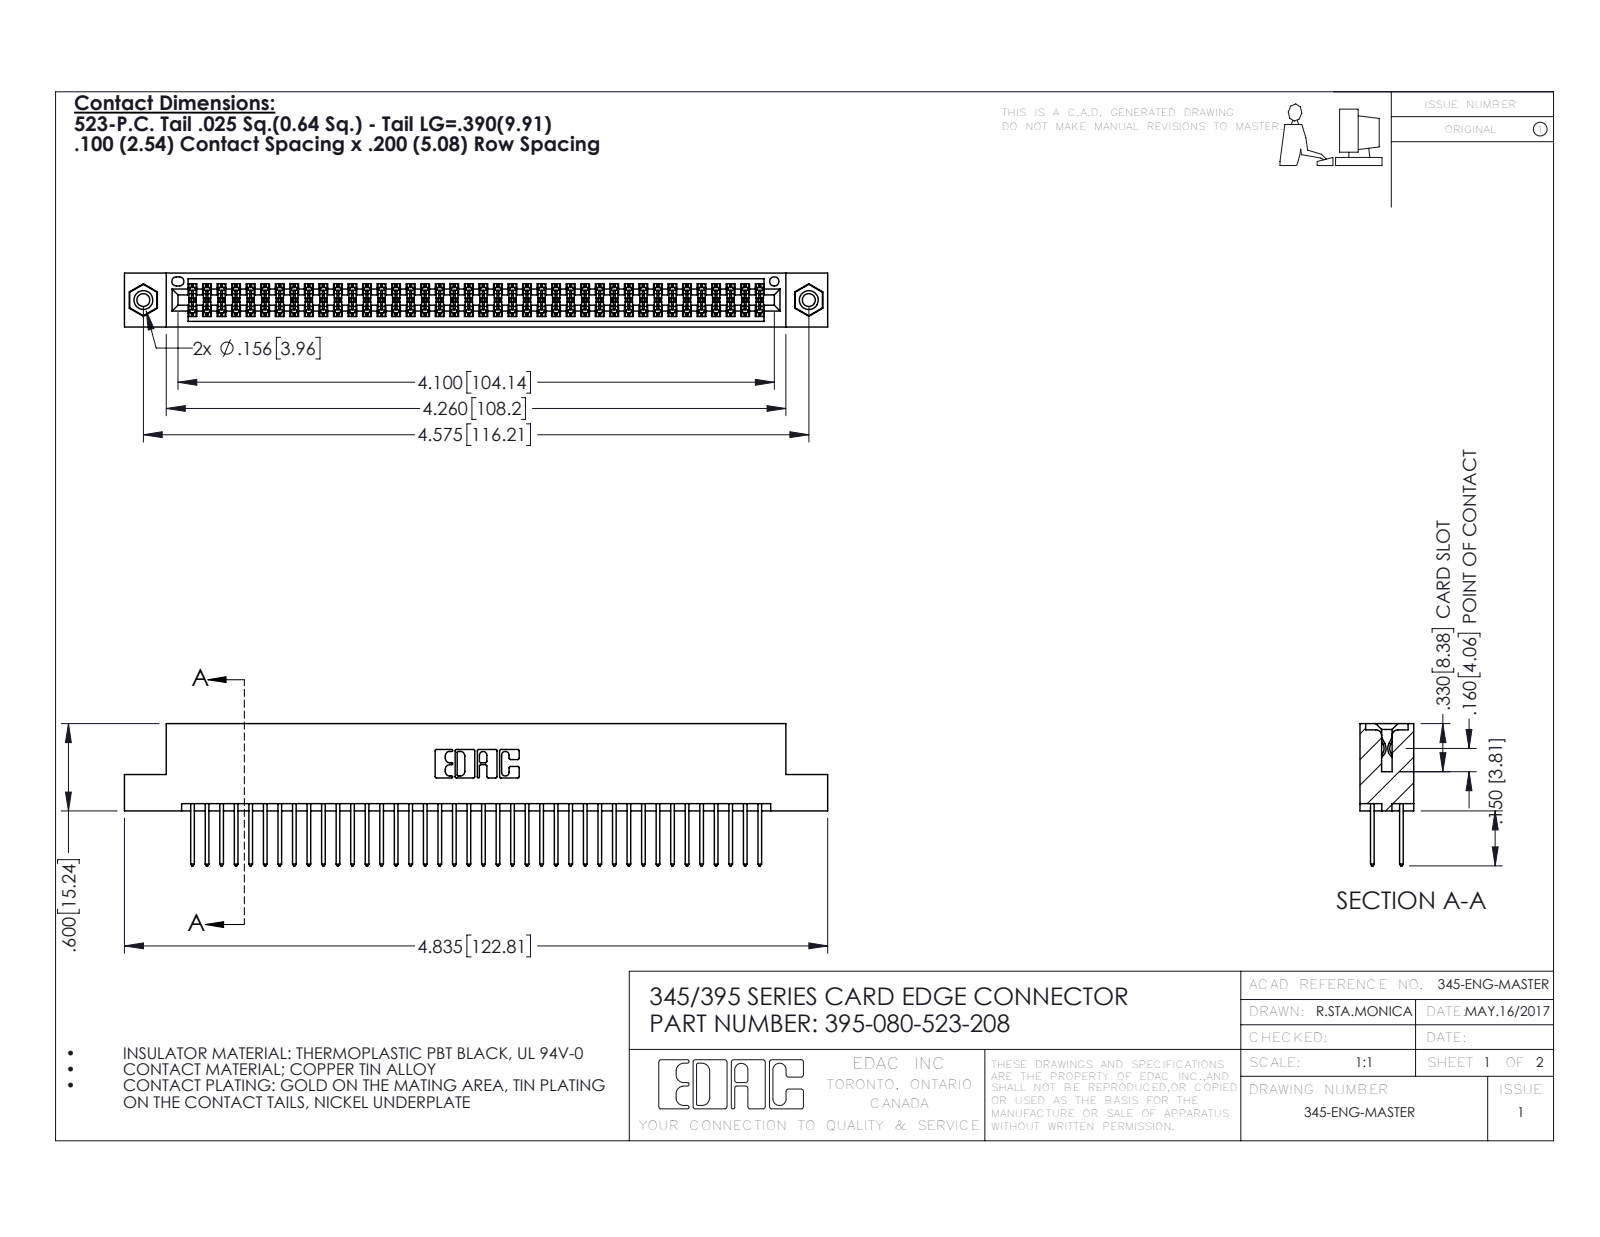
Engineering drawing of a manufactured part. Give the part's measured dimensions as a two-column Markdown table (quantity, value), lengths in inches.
| quantity | value |
| --- | --- |
| part name | 345-292-001_345-293-123; 345 Part_Flush Mounting Lugs - 0.156 Dia-TI; 395-080-523-208; 345-250-001_345-250-003-102 |
| STEP written by | SolidWorks 2016 (CONFIG_CONTROL_DESIGN) |
| units | inches |
| bodies | 83 solids, 4186 faces (2752 planar, 1418 cylindrical, 16 other) |
| overall size | 4.835 × 0.977 × 0.37 |
| volume | 0.736 in³ |
| surface area | 28.75 in² |
| round holes (diameter × count) | 0.089 × 2, 0.125 × 2, 0.156 × 2, 0.064 × 1 |
| round bosses / shafts (diameter × count) | 0.155 × 2 |
| partial cylindrical surfaces (radius × count) | 0.006 × 120, 0.01 × 80, 0.01 × 22, 0.007 × 6, 0.031 × 6, 0.026 × 3, 0.014 × 2, 0.019 × 2 |
| main face-to-face distances | 0.072, 0.298, 0.2, 0.098, 0.272, 0.025, 0.37, 0.225, 0.175, 0.149 |
| hole center spacings | 0.27, 4.339, 4.575 |
